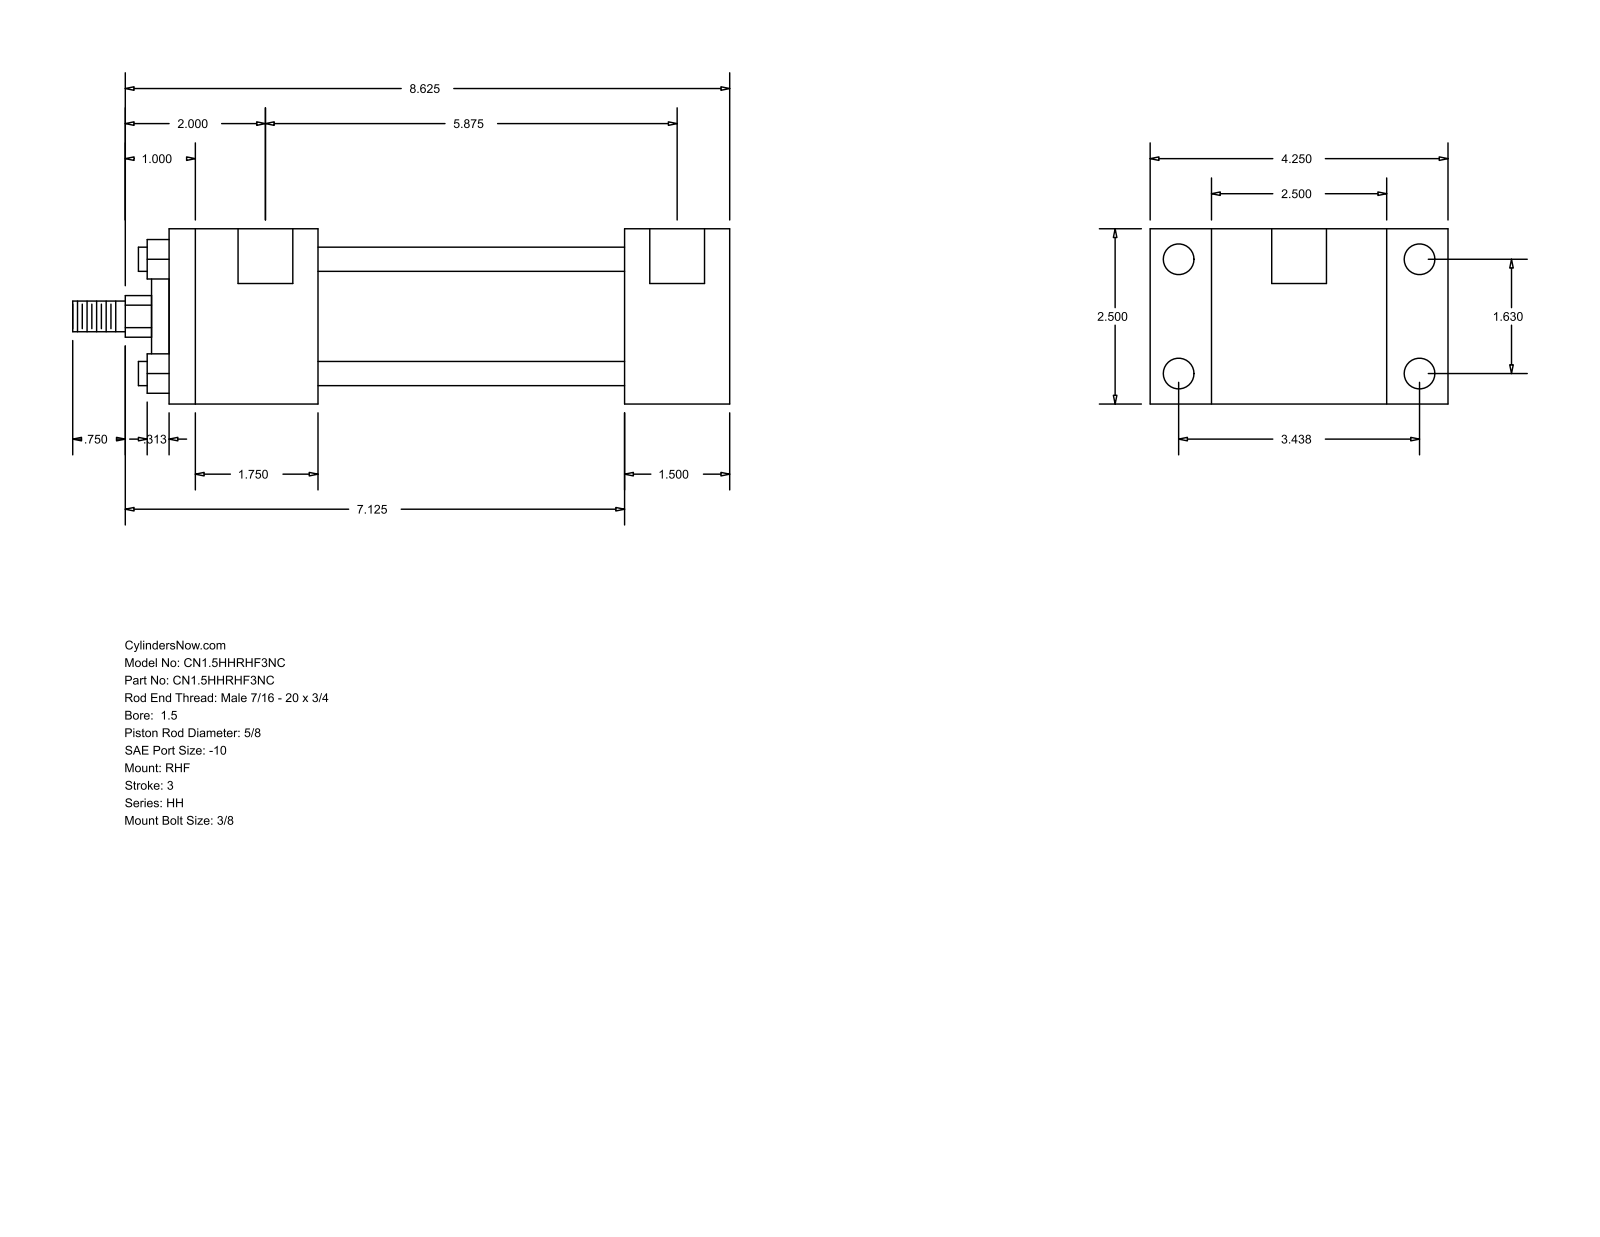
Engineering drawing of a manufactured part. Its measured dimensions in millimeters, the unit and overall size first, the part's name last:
Units: millimetres
Overall size (bounding box): 238.12 × 107.95 × 63.5
Round holes (diameter × count): ⌀5.56 ×4, ⌀11.13 ×4, ⌀19.84 ×2
Round bosses / shafts (diameter × count): ⌀8.76 ×4, ⌀44.45 ×1, ⌀28.57 ×1, ⌀15.88 ×1, ⌀11.11 ×1
Partial cylindrical surfaces — rounded edges, fillets, slot ends (radius × count): R7.54 ×1
Main face-to-face distances: 63.5, 38.1, 22.23, 85.73, 165.09, 203.19, 107.96, 53.97, 111.12, 149.22
Hole centre spacings: 41.4, 87.32, 96.64, 152.4, 1.58, 1.59, 149.23, 150.81
Bodies: 0 solids, 88 faces (60 planar, 28 cylindrical, 0 other)
Part name (STEP PRODUCT): HH_RHF__0150_0.625
STEP written by: GSSL Pune (CONFIG_CONTROL_DESIGN)
